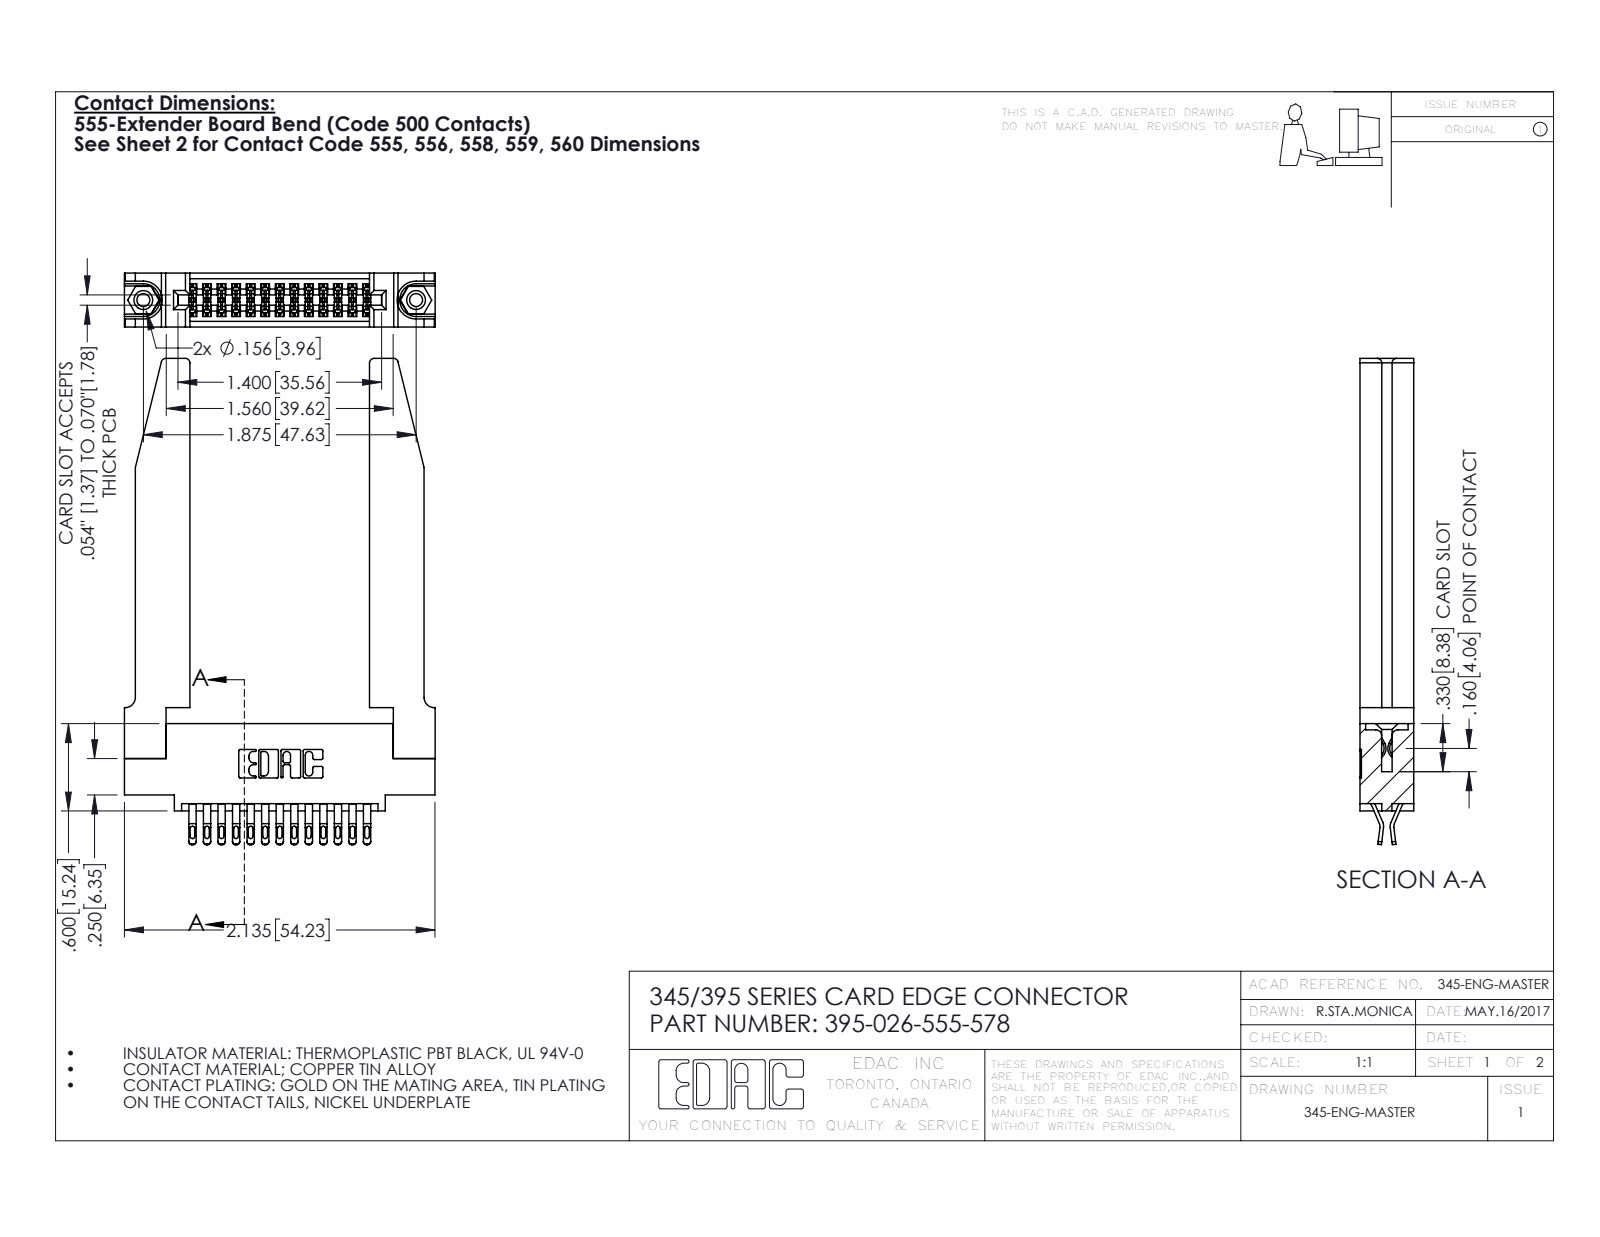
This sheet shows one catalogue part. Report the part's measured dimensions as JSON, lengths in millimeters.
{"part_name": "345-250-001_345-250-001-102; 345-220-078_345-220-078; 345 Part_0.110 Offset - 0.156 Dia-TH; 395-026-555-578 (+1 more)", "step_written_by": "SolidWorks 2016 (CONFIG_CONTROL_DESIGN)", "units": "millimeters", "bodies": {"solids": 31, "faces": 1820, "planar": 1032, "cylindrical": 736, "other": 52}, "overall_size": [84.9, 54.3, 9.4], "volume_mm3": 12800, "surface_area_mm2": 14030, "round_holes": [[2.3, 2], [3.2, 2], [4, 2], [1.6, 1]], "round_bosses_or_shafts": [[3.9, 2]], "partial_cylinders_radius": [[0.4, 65], [0.5, 52], [0.2, 39], [0.3, 22], [0.8, 8], [0.2, 6], [0.8, 6], [0.7, 3]], "face_to_face_distances": [9.4, 1.8, 7.6, 3.8, 3.8, 0.6, 5.6, 2, 31.4, 5.1], "hole_center_spacings": [6.9, 41.7, 47.6]}
